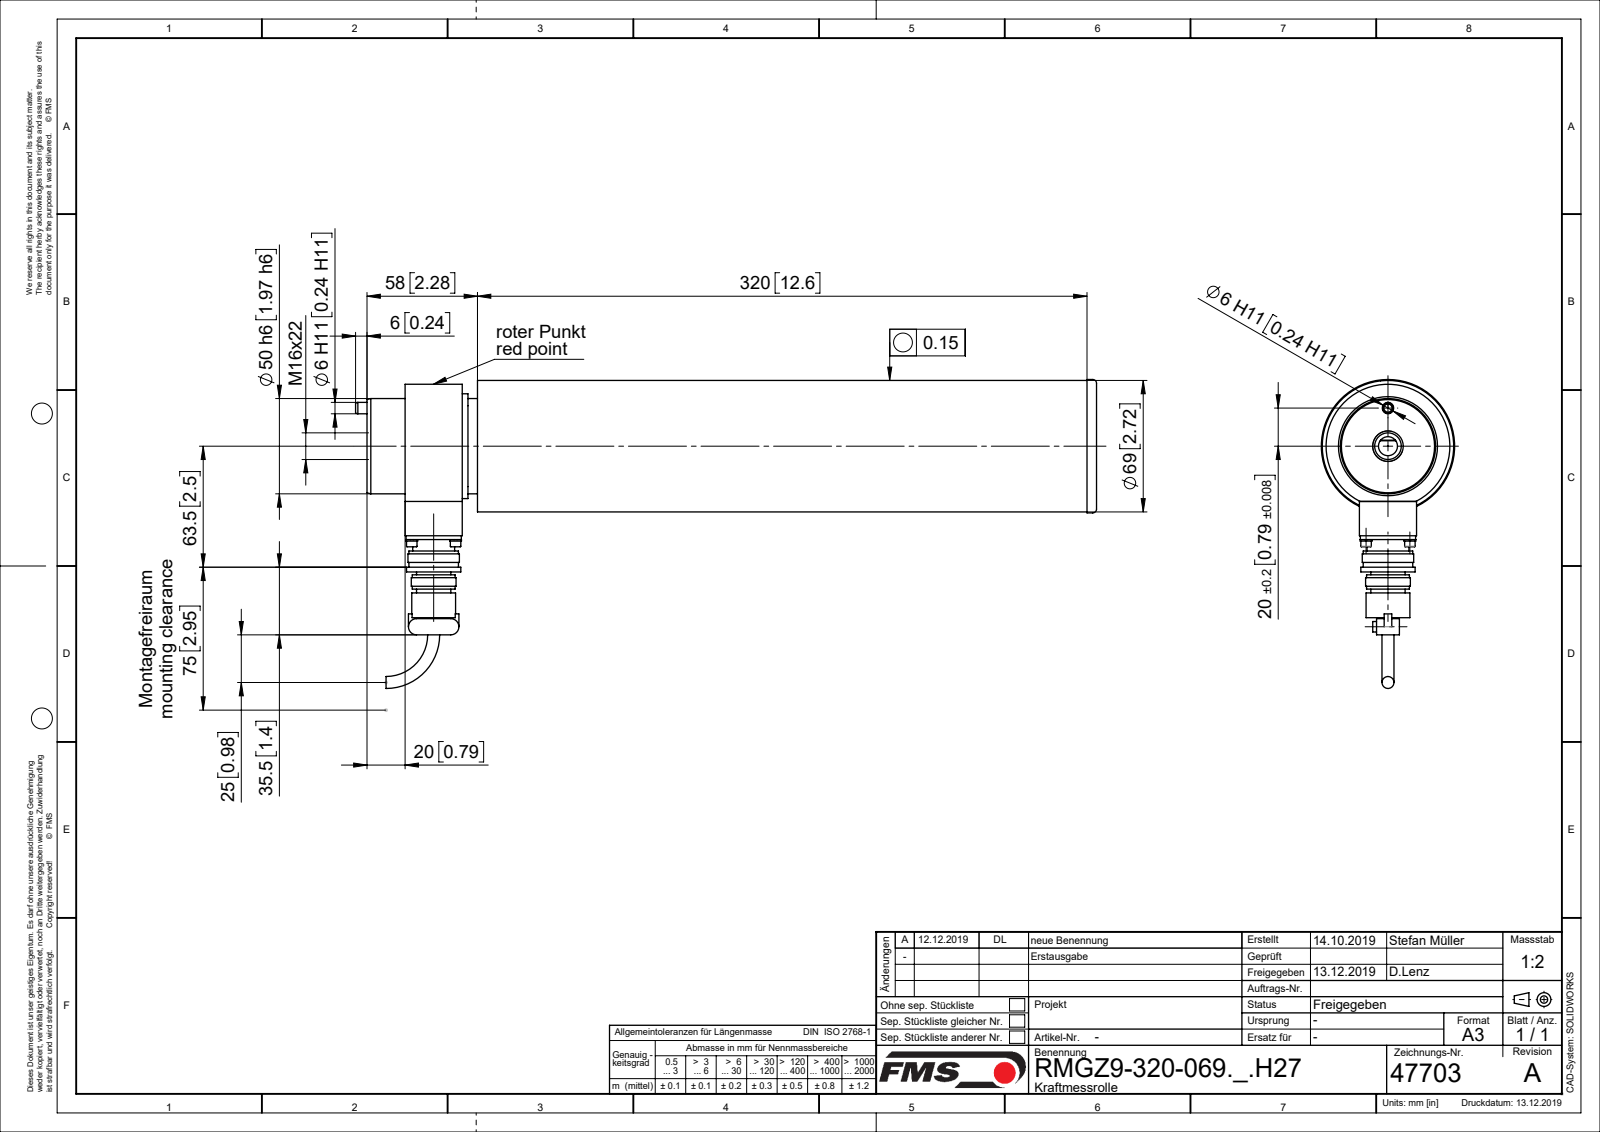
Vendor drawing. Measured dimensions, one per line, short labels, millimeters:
name: R47703; R47708; TEIL1; R4772604 (+8 more)
written by: Mechanical Desktop 2007 (CONFIG_CONTROL_DESIGN)
unit: mm
bodies: 19 solids, 441 faces (136 planar, 207 cylindrical, 98 other)
size: 383 × 162.15 × 70
volume: 830 941 mm³; area: 284 256 mm²
holes: 8× ⌀3.4, 4× ⌀2.3, 4× ⌀3.2, 1× ⌀10, 1× ⌀12, 1× ⌀13, 1× ⌀16, 1× ⌀17, 1× ⌀21, 1× ⌀23, 1× ⌀25, 1× ⌀26
bosses: 6× ⌀5.5, 4× ⌀6.2, 4× ⌀3, 4× ⌀2.5, 1× ⌀70, 1× ⌀69, 1× ⌀65, 1× ⌀59
rounds: 2× R4.25, 1× R17.5
face distances: 35, 50, 5, 2.5, 330, 30, 325, 18, 3, 13
hole spacings: 23, 16.26, 32.53, 16.27, 22.99, 23.01, 32.52, 16.05
